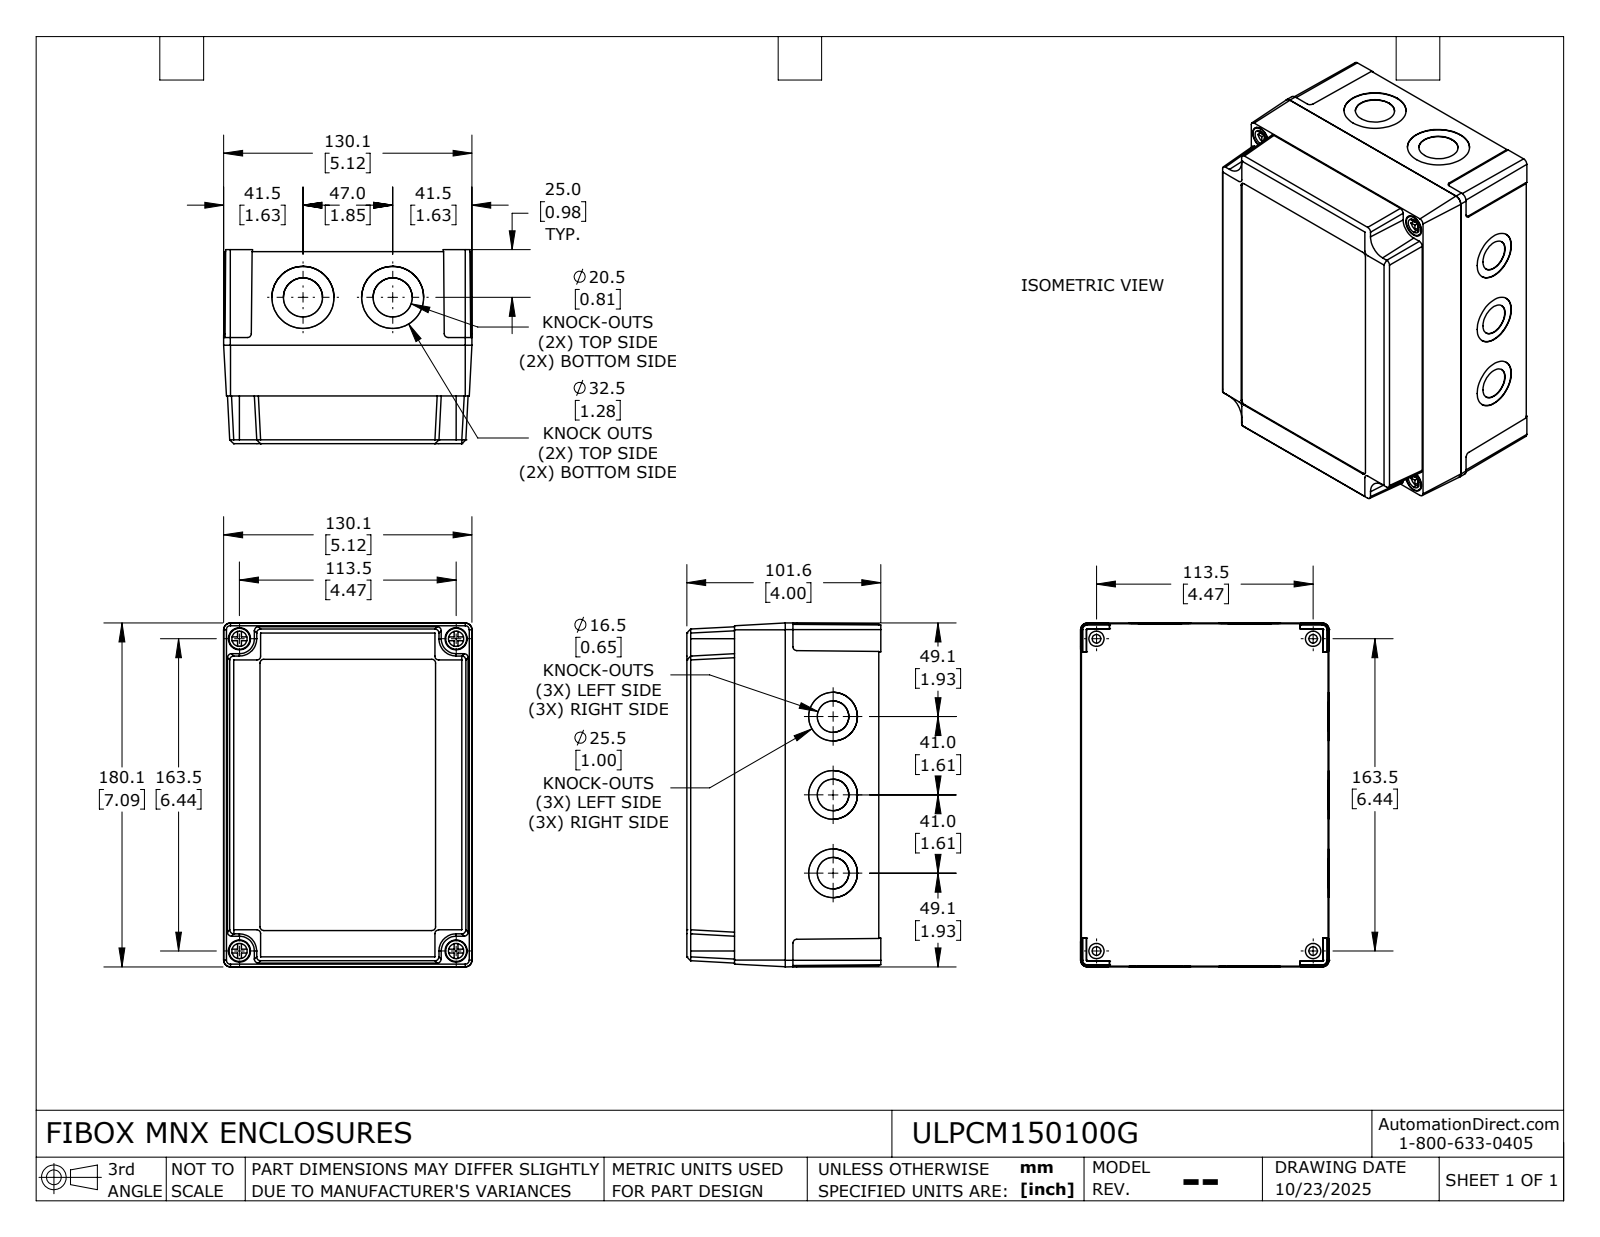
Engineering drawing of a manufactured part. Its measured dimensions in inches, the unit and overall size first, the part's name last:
Units: inches
Overall size (bounding box): 7.091 × 5.122 × 4
Round holes (diameter × count): ⌀0.126 ×8, ⌀0.157 ×8, ⌀0.65 ×6, ⌀1.004 ×6, ⌀0.177 ×4, ⌀0.315 ×4, ⌀0.457 ×4, ⌀0.807 ×4, ⌀1.28 ×4
Round bosses / shafts (diameter × count): ⌀0.315 ×8, ⌀0.098 ×8, ⌀0.433 ×4, ⌀0.283 ×4
Partial cylindrical surfaces — rounded edges, fillets, slot ends (radius × count): R0.079 ×8, R0.083 ×8, R0.056 ×6, R0.021 ×4, R0.197 ×4, R0.023 ×2
Main face-to-face distances: 3.862, 0.118, 3.744, 0.165, 0.079, 3.823, 3.941, 0.055, 0.078, 0.098
Hole centre spacings: 1.333, 1.614, 1.939, 1.969, 2.281, 3.252, 3.276, 4.054
Volume: 19.99 in³ · Surface area: 344 in²
Bodies: 6 solids, 581 faces (335 planar, 200 cylindrical, 46 other)
Part name (STEP PRODUCT): ULPCM150100G_Default
STEP written by: SolidWorks 2024 (CONFIG_CONTROL_DESIGN)
